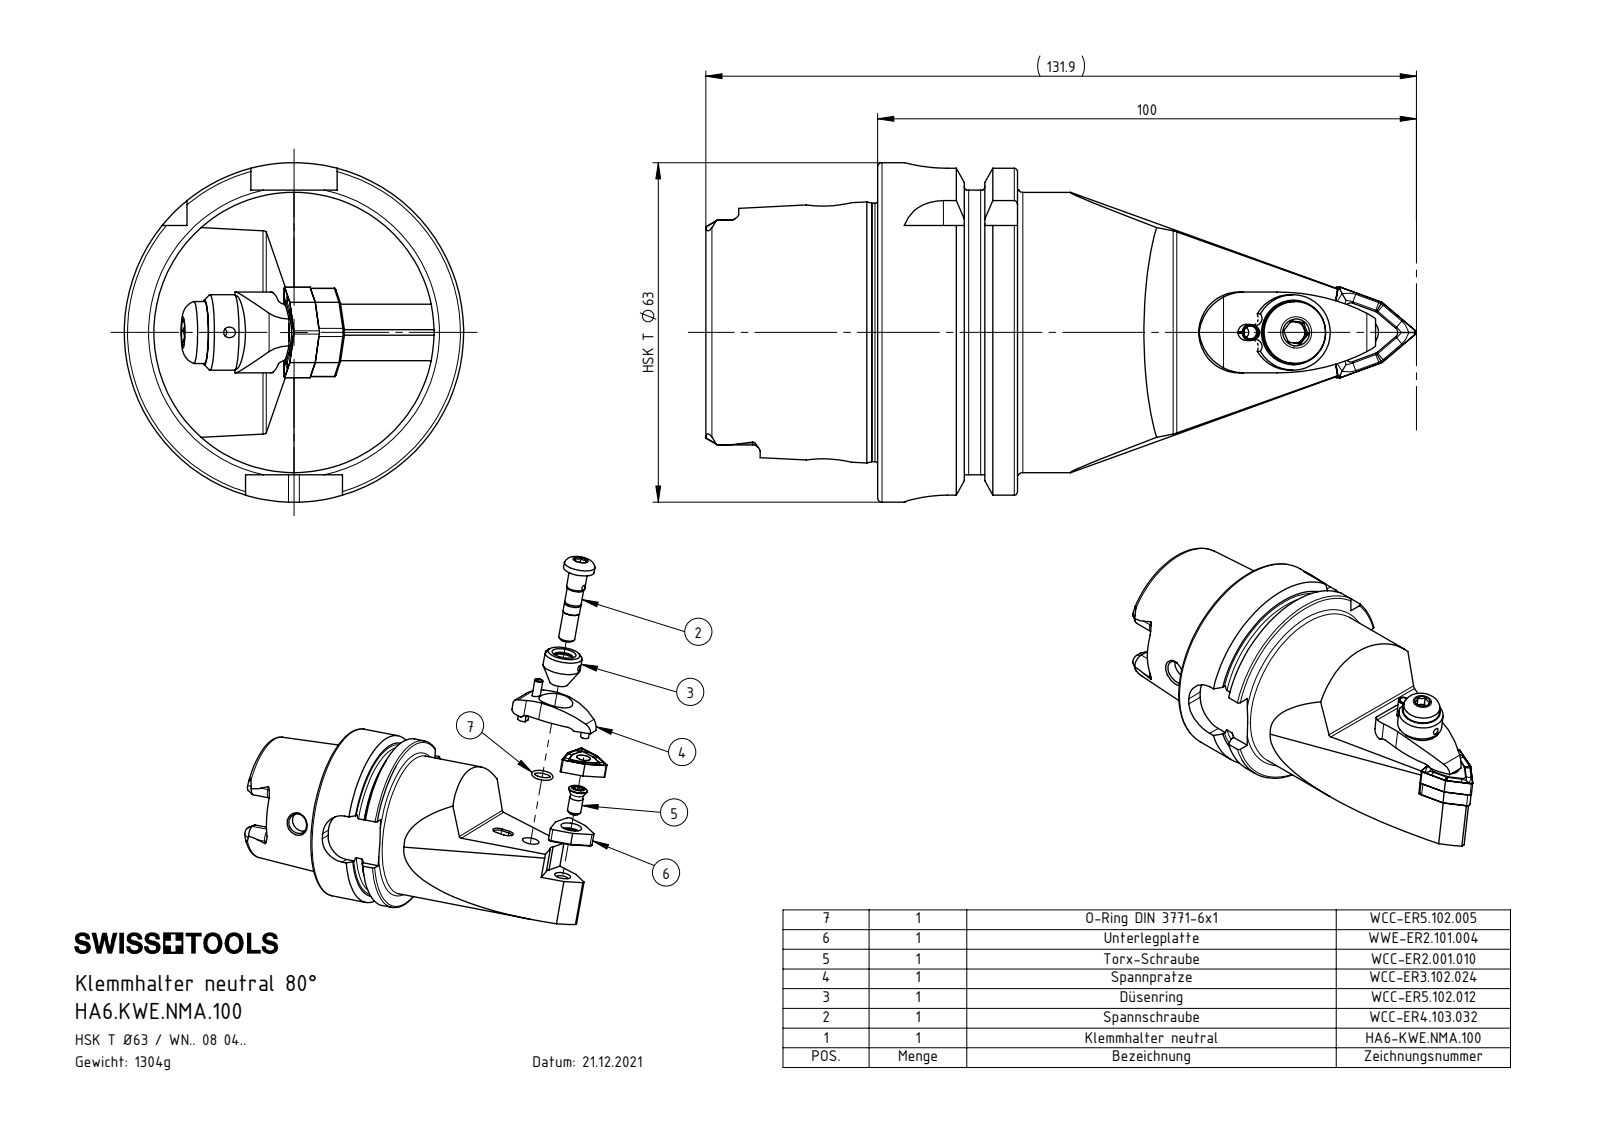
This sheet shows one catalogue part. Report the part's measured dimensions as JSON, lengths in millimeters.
{"part_name": "WCC-ER5.102.005_A; WCC-ER4.103.032_A; ISO 13337 - 3 x 12_PreviewCfg; WWE-ER2.101.004_A (+7 more)", "step_written_by": "SolidWorks 2017 (AUTOMOTIVE_DESIGN)", "units": "millimeters", "bodies": {"solids": 11, "faces": 501, "planar": 135, "cylindrical": 158, "other": 208}, "overall_size": [131.9, 63, 63], "volume_mm3": 165594, "surface_area_mm2": 36430, "round_holes": [[5, 4], [2, 3], [7, 2], [2.4, 1], [3, 1], [4.2, 1], [5.16, 1], [6, 1], [6.2, 1], [6.7, 1], [7.5, 1], [7.8, 1]], "round_bosses_or_shafts": [[6, 2], [3, 2], [63, 1], [54.95, 1], [52, 1], [47.94, 1], [14, 1], [11.5, 1]], "partial_cylinders_radius": [[0.39, 6], [1.4, 6], [2.88, 4], [8, 4], [0.4, 3], [0.69, 3], [0.69, 3], [1, 3]], "face_to_face_distances": [25.95, 16, 9.95, 31.9, 41.85, 57.85, 52.8, 21.8, 11.85, 4.46], "hole_center_spacings": [8, 15, 23, 8.2, 14.8]}
